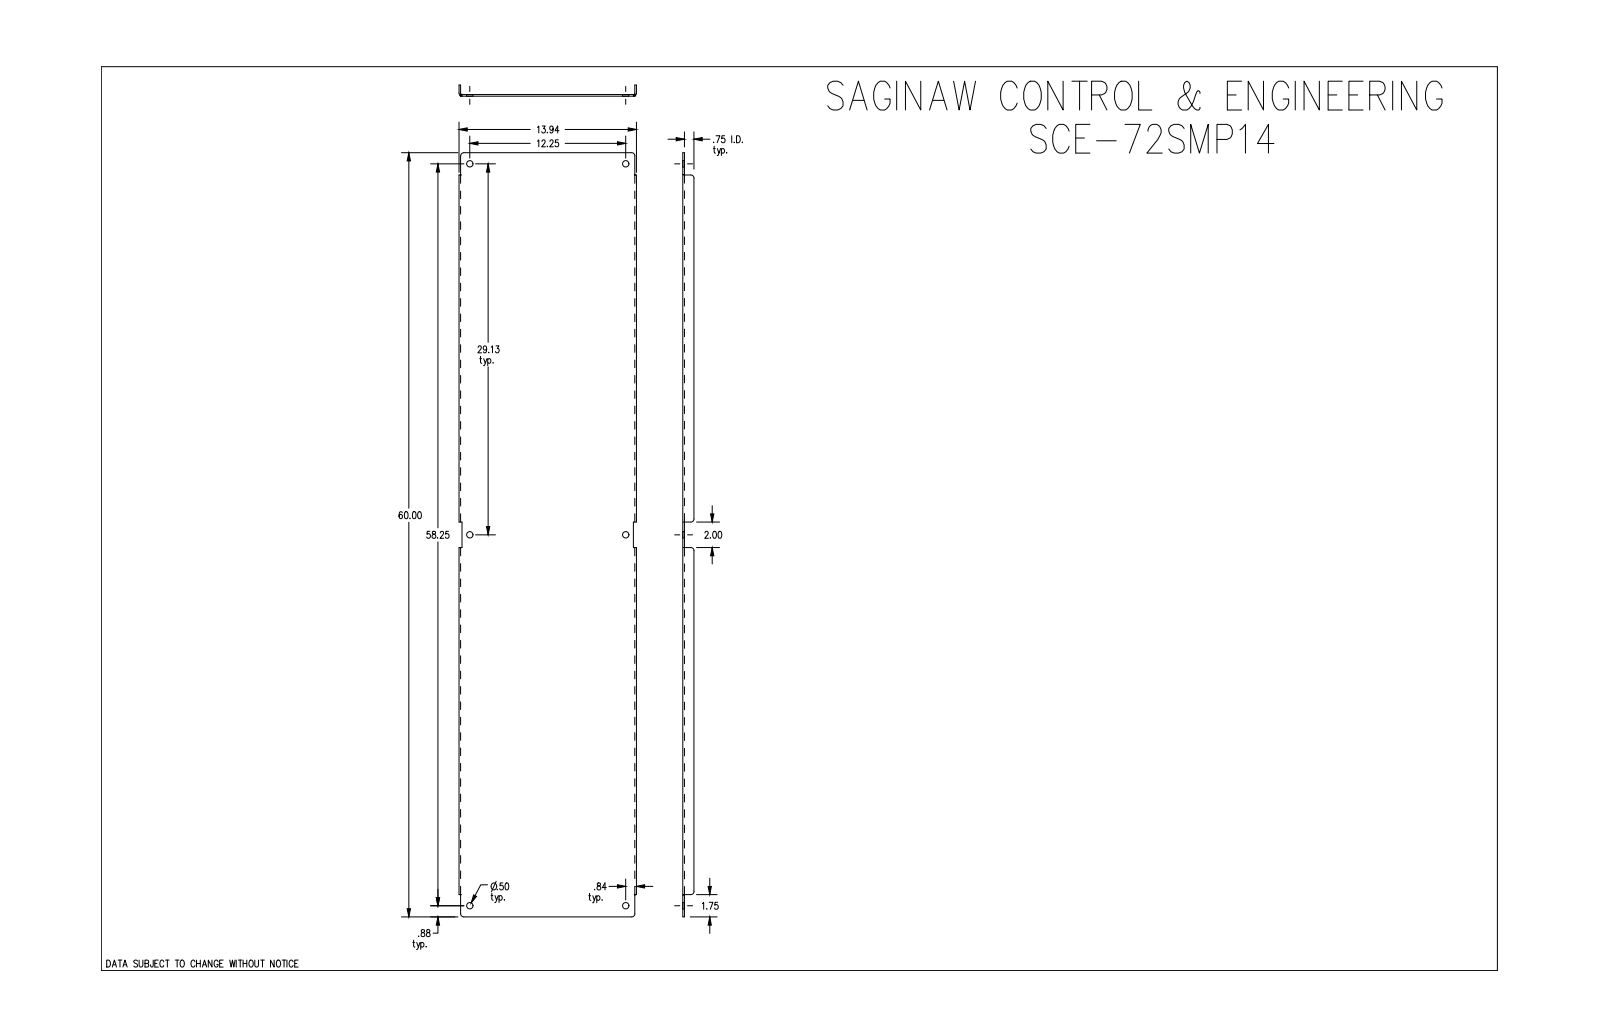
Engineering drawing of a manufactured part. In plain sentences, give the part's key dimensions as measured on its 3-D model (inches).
The part is named "SCE-72SMP14". Its 3-D file was written by "SolidWorks 2019 (CONFIG_CONTROL_DESIGN)". It is 1 solid with 68 faces: 30 planar, 26 cylindrical and 12 other. Overall it measures 60 by 13.938 by 0.875 inches. Its volume is 113.3 cubic inches and its surface area 1 834 square inches. Round holes: 6 of diameter 0.5. Partial cylindrical surfaces (rounded edges, fillets, slot ends): 8 of radius 0.25, 2 of radius 0.112, 2 of radius 0.237. The main face-to-face distances are 0.125, 0.125, 13.813, 13.687, 13.938, 0.75, 0.875, 60, 0.237, 13.701. The hole center spacings are 29.125, 31.596, 12.25, 58.25, 59.524.
